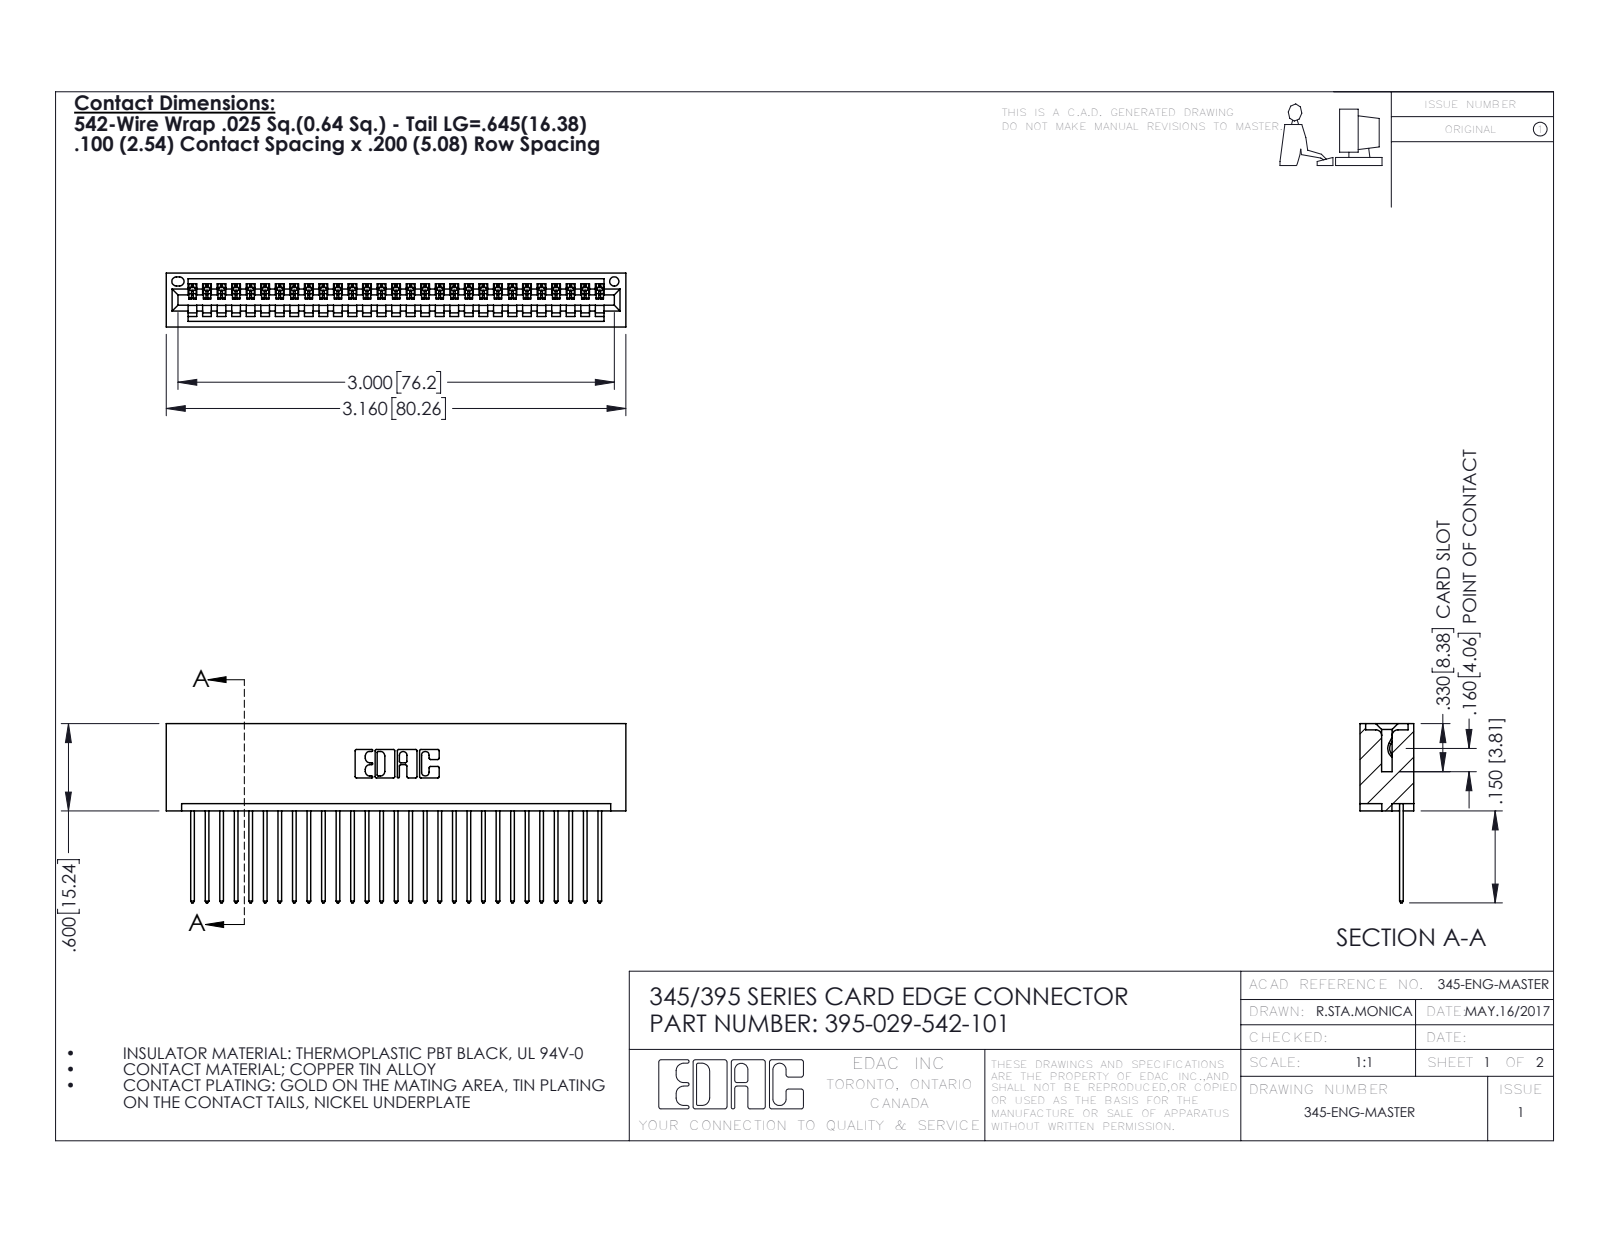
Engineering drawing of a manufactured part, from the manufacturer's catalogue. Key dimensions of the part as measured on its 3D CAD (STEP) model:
Part name (STEP PRODUCT): 345-292-001_345-293-142; 395-029-542-101; 345 Part_No Mounting Lugs
STEP written by: SolidWorks 2016 (CONFIG_CONTROL_DESIGN)
Units: inches
Bodies: 30 solids, 1800 faces (1236 planar, 564 cylindrical, 0 other)
Overall size (bounding box): 3.16 × 1.232 × 0.37
Volume: 0.498 in³ · Surface area: 17.47 in²
Round holes (diameter × count): ⌀0.064 ×1
Partial cylindrical surfaces — rounded edges, fillets, slot ends (radius × count): R0.006 ×58, R0.01 ×58, R0.01 ×22, R0.007 ×6, R0.031 ×6, R0.026 ×3, R0.031 ×2, R0.04 ×2
Main face-to-face distances: 0.072, 0.298, 0.098, 0.272, 0.025, 0.2, 0.37, 0.225, 0.149, 0.072
